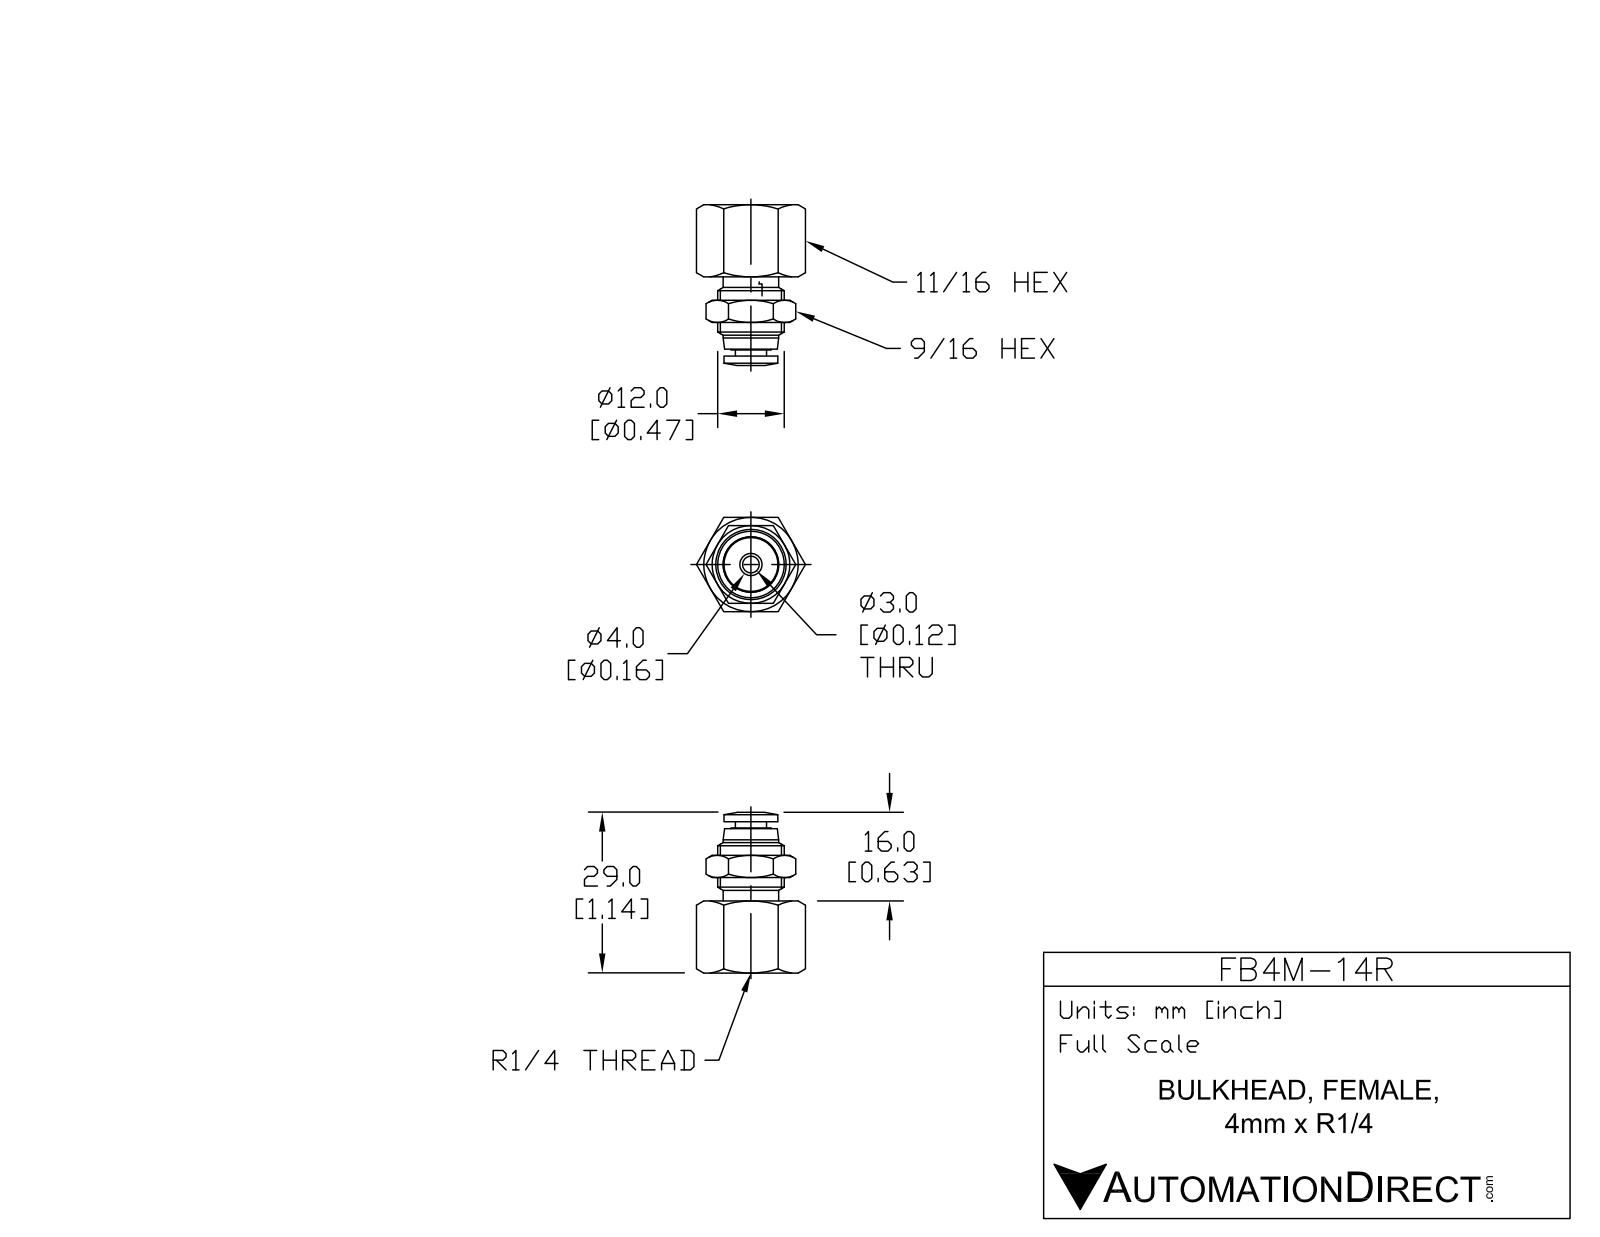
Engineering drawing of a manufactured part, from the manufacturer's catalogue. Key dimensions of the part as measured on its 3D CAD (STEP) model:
Part name (STEP PRODUCT): FB4M-14R
STEP written by: SolidWorks 2015 (AUTOMOTIVE_DESIGN)
Units: inches
Bodies: 1 solid, 76 faces (22 planar, 18 cylindrical, 36 other)
Overall size (bounding box): 1.144 × 0.773 × 0.669
Volume: 0.199 in³ · Surface area: 4.161 in²
Round holes (diameter × count): ⌀0.118 ×1, ⌀0.169 ×1
Round bosses / shafts (diameter × count): ⌀0.472 ×1, ⌀0.394 ×1, ⌀0.382 ×1, ⌀0.283 ×1, ⌀0.22 ×1
Main face-to-face distances: 0.669, 0.059, 0.61, 0.079, 0.512, 0.433, 0.551, 0.565, 1.077, 0.644
